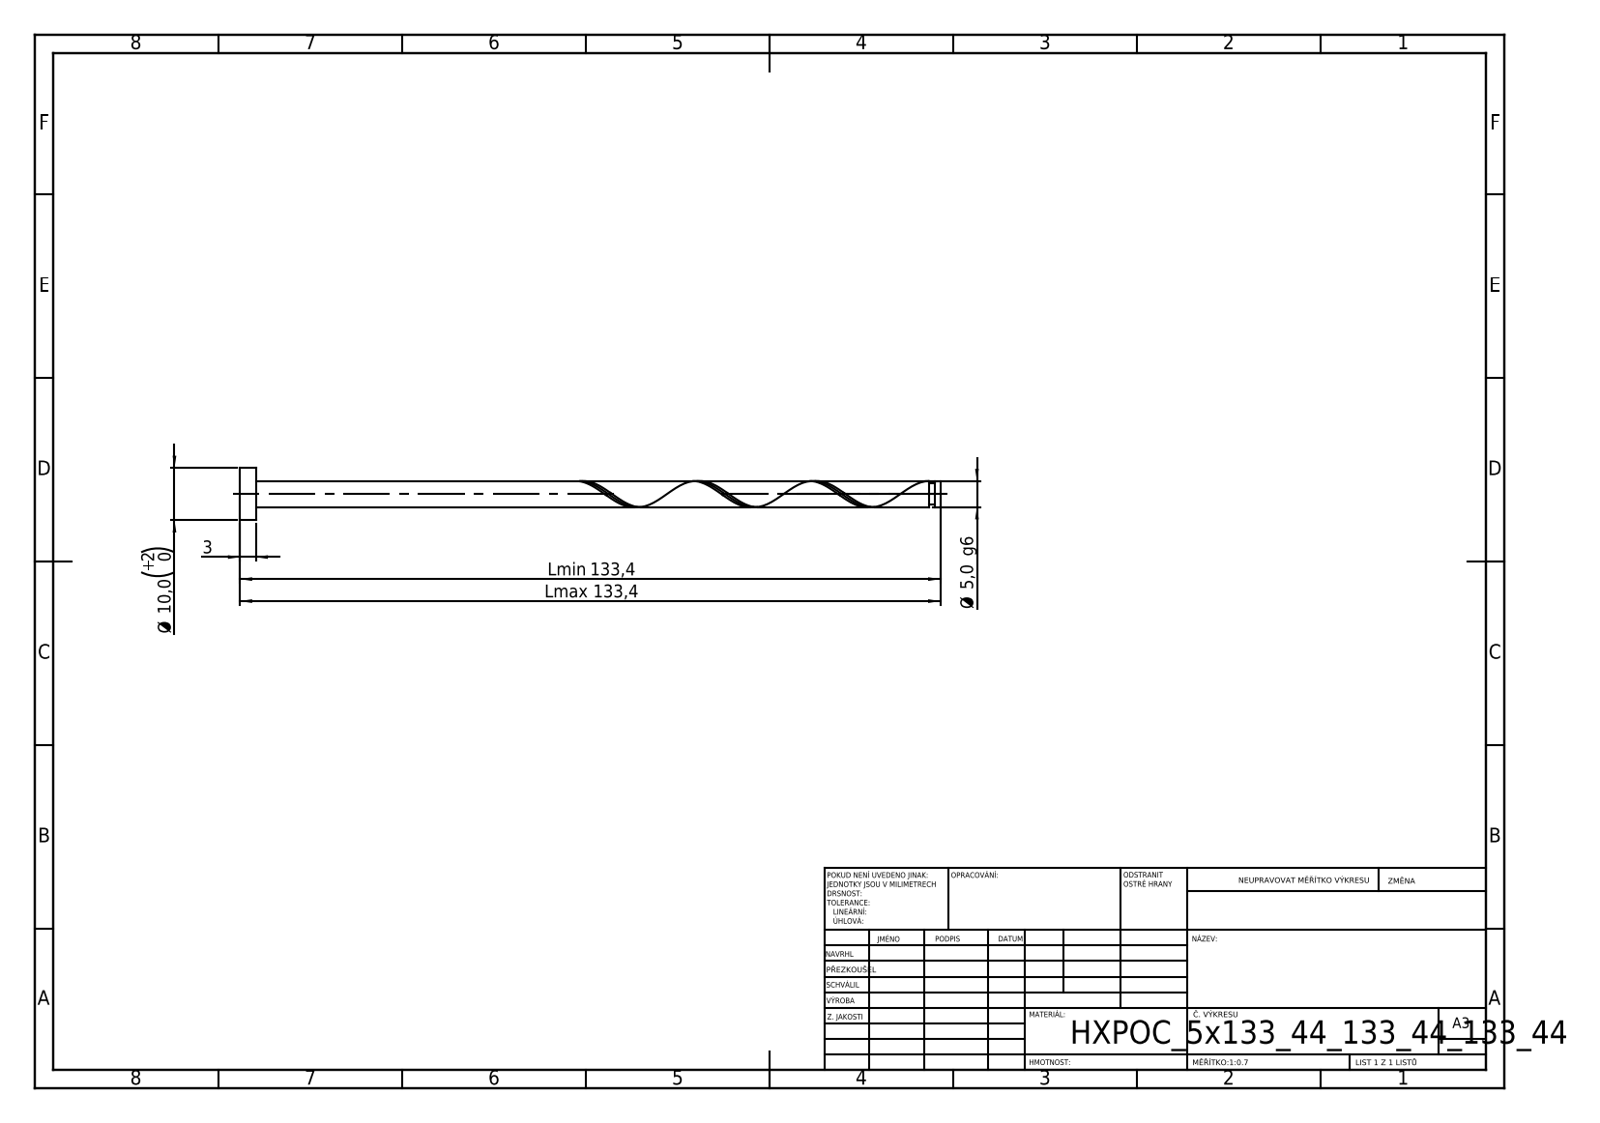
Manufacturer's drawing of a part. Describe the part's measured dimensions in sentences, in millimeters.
Its 3-D file was written by "SolidWorks 2019 (CONFIG_CONTROL_DESIGN)". It is 1 solid with 21 faces: 6 planar, 14 cylindrical and 1 other. Overall it measures 133.44 by 10 by 10 millimeters. Its volume is 2 765 cubic millimeters and its surface area 2 353 square millimeters. Round bosses or shafts: 1 of diameter 10, 1 of diameter 5, 1 of diameter 4. The main face-to-face distances are 3, 133.44, 130.44, 132.38, 129.38, 1.06, 131.38, 128.38, 1, 2.06.
